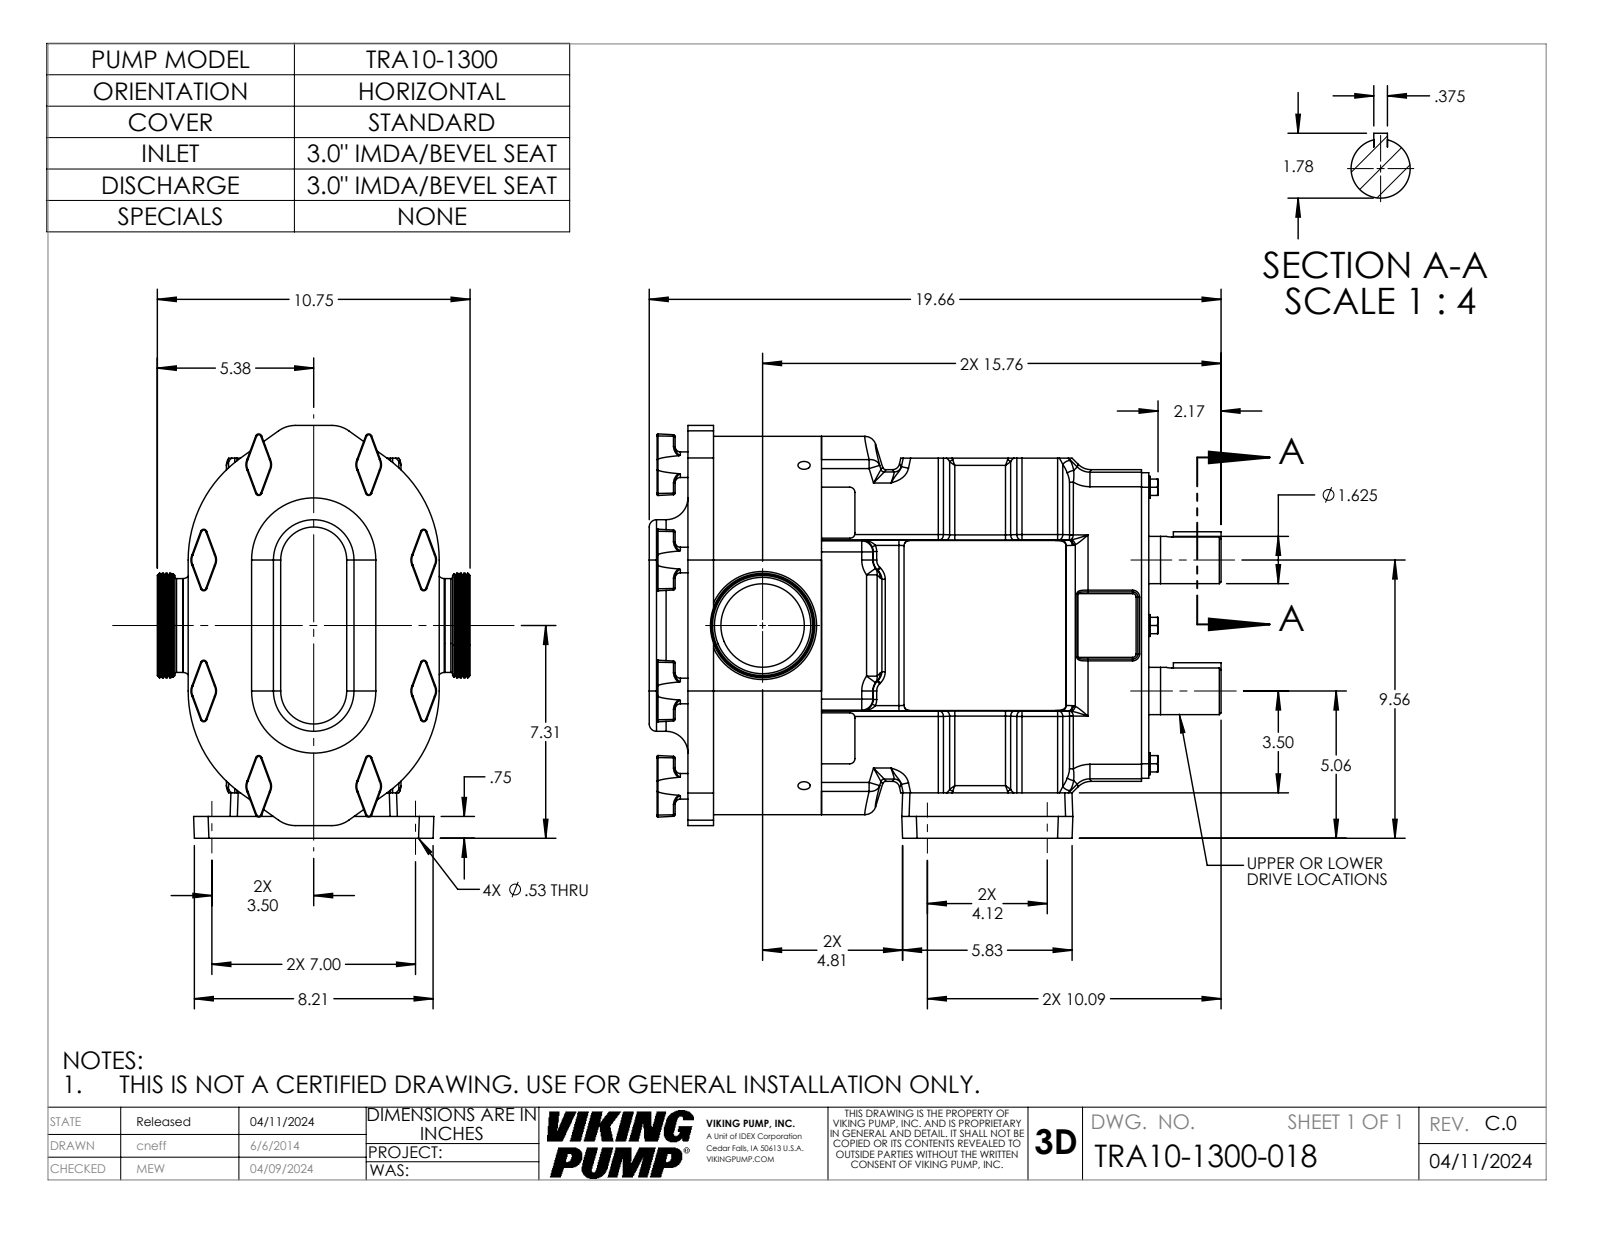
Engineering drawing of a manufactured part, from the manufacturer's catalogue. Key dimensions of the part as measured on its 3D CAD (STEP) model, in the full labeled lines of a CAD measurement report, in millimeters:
Part name (STEP PRODUCT): TRA10-0600-COVER-STD; TRA10-1300-BODY; TRA10-0600-GEARBOX-H; TRA10-1300-018 (+1 more)
STEP written by: SolidWorks 2022 (AUTOMOTIVE_DESIGN)
Units: millimetres
Bodies: 5 solids, 1139 faces (287 planar, 412 cylindrical, 440 other)
Overall size (bounding box): 499.3 × 360.3 × 273.1
Volume: 20 910 000 mm³ · Surface area: 896 800 mm²
Round holes (diameter × count): ⌀8.4 ×4, ⌀13.5 ×4, ⌀72.8 ×1
Round bosses / shafts (diameter × count): ⌀22.4 ×8, ⌀19.1 ×6, ⌀41.2 ×2, ⌀91.1 ×1, ⌀87.4 ×1, ⌀81.9 ×1
Partial cylindrical surfaces — rounded edges, fillets, slot ends (radius × count): R4.6 ×44, R1.5 ×43, R0.8 ×32, R6.4 ×32, R9.7 ×28, R3 ×24, R12.7 ×20, R9.5 ×12
Main face-to-face distances: 94.3, 12.7, 22.4, 116.6, 9.1, 402.4, 380, 285.8, 165.1, 19.1
Hole centre spacings: 73.5, 104.6, 177.8, 206.3
